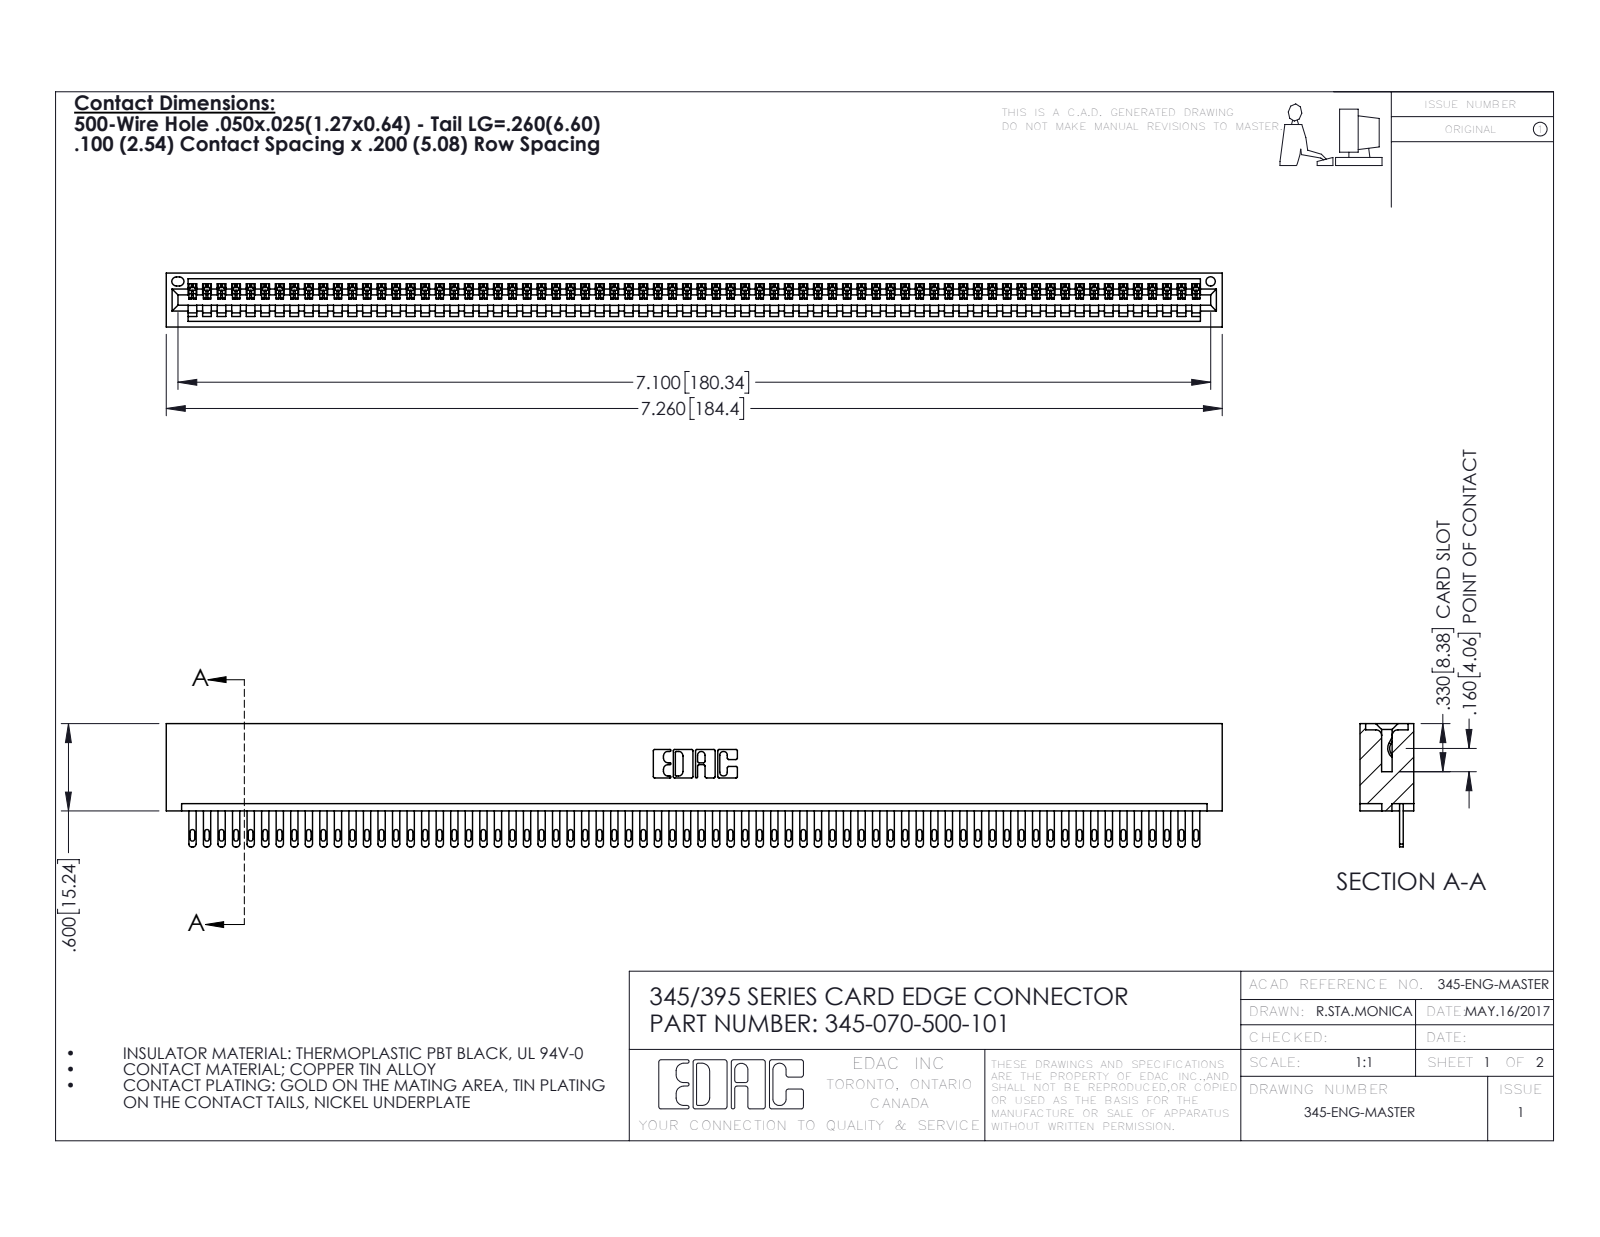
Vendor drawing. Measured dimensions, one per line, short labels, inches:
name: 345 Part_No Mounting Lugs; 345-292-001_345-293-100; 345-070-500-101
written by: SolidWorks 2016 (CONFIG_CONTROL_DESIGN)
unit: in
bodies: 71 solids, 3898 faces (2456 planar, 1442 cylindrical, 0 other)
size: 7.26 × 0.847 × 0.37
volume: 1.121 in³; area: 38.97 in²
holes: 1× ⌀0.064
rounds: 140× R0.006, 140× R0.016, 140× R0.02, 22× R0.01, 6× R0.007, 6× R0.031, 3× R0.026, 2× R0.031
face distances: 0.072, 0.298, 0.37, 0.098, 0.272, 0.025, 0.2, 0.225, 0.149, 0.072
